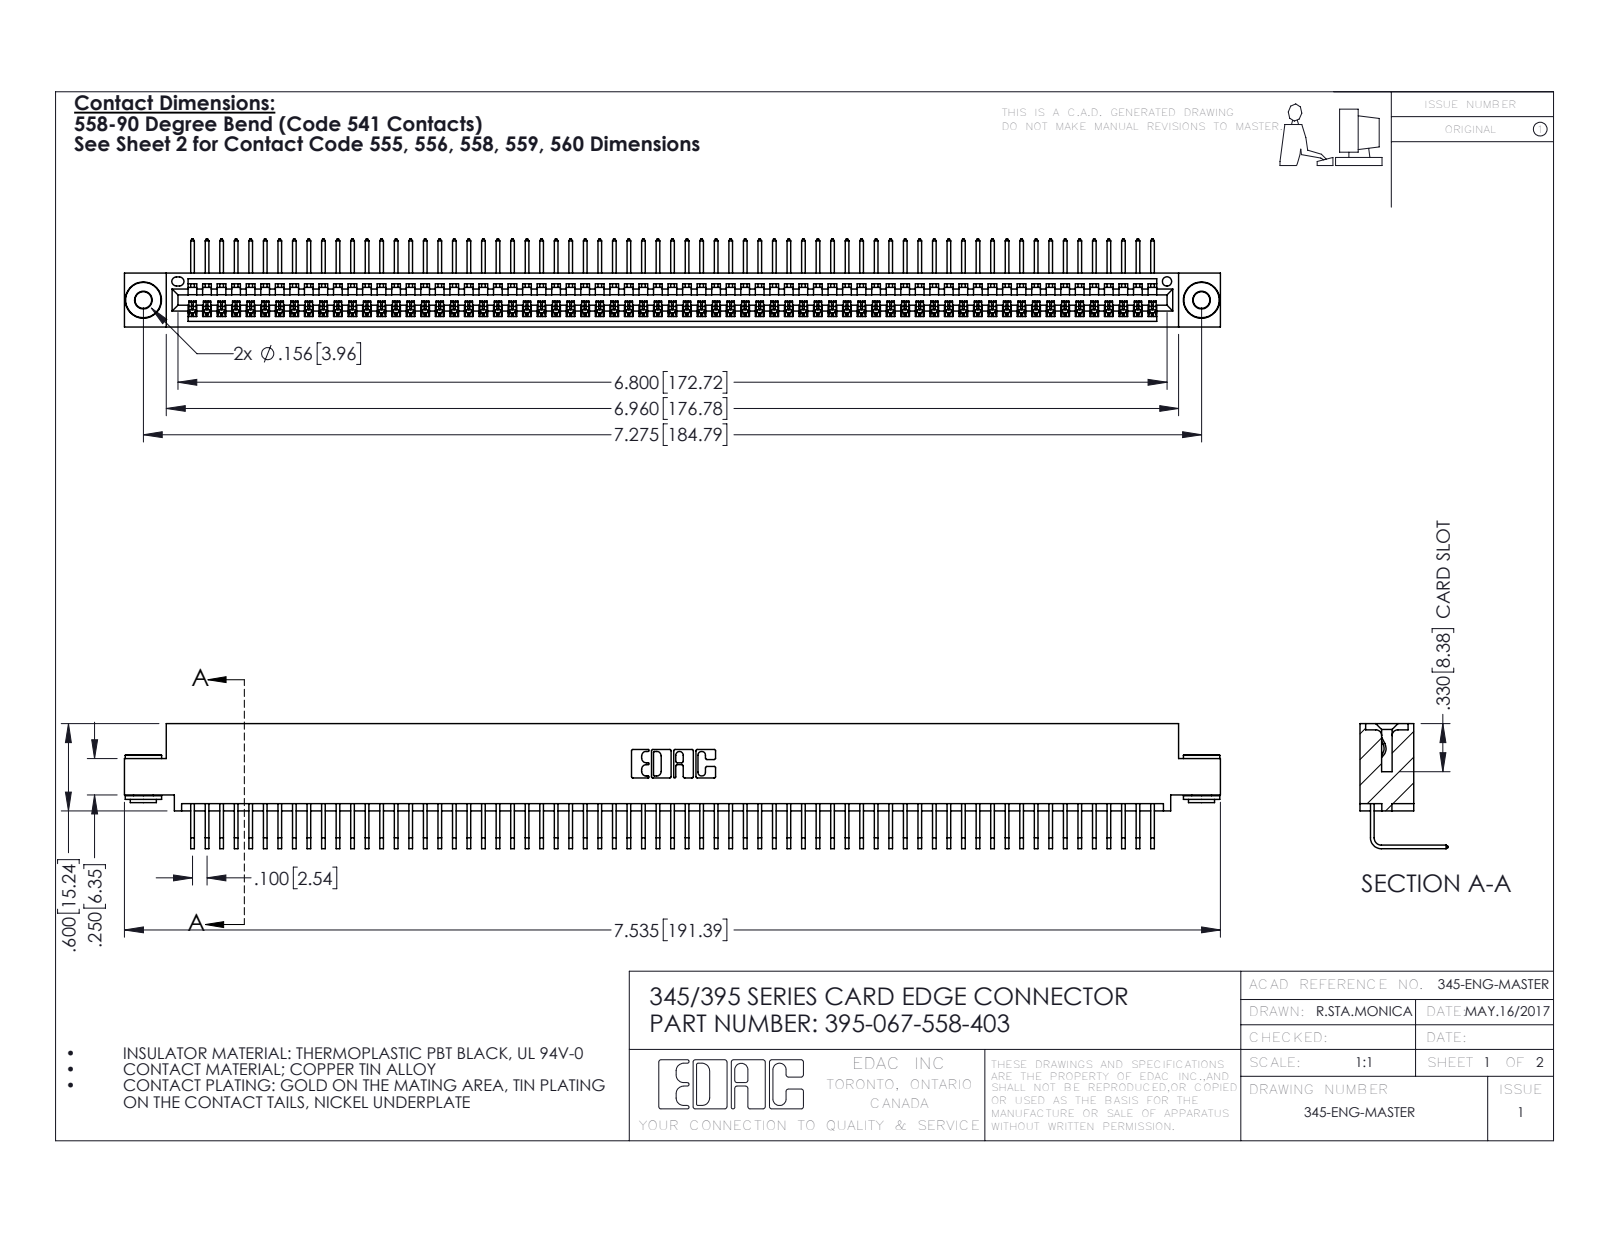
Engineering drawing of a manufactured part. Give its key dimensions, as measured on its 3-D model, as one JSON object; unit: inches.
{"part_name": "395-067-558-403; 345-292-001_558 Tail - 2; 345 Part_0.110 Offset - 0.156 Dia-TH; 345-250-002_345-250-002-102", "step_written_by": "SolidWorks 2016 (CONFIG_CONTROL_DESIGN)", "units": "inches", "bodies": {"solids": 70, "faces": 4188, "planar": 2908, "cylindrical": 1272, "other": 8}, "overall_size": [7.535, 0.859, 0.605], "volume_in3": 1.132, "surface_area_in2": 41.23, "round_holes": [[0.116, 2], [0.156, 2], [0.064, 1]], "round_bosses_or_shafts": [[0.25, 2], [0.18, 2], [0.136, 2]], "partial_cylinders_radius": [[0.006, 134], [0.01, 22], [0.007, 6], [0.031, 6], [0.026, 3], [0.031, 2], [0.04, 2], [0.014, 1]], "face_to_face_distances": [0.072, 0.298, 0.37, 0.2, 0.025, 0.098, 0.272, 0.225, 0.149, 0.072], "hole_center_spacings": [0.27, 7.039, 7.275]}
